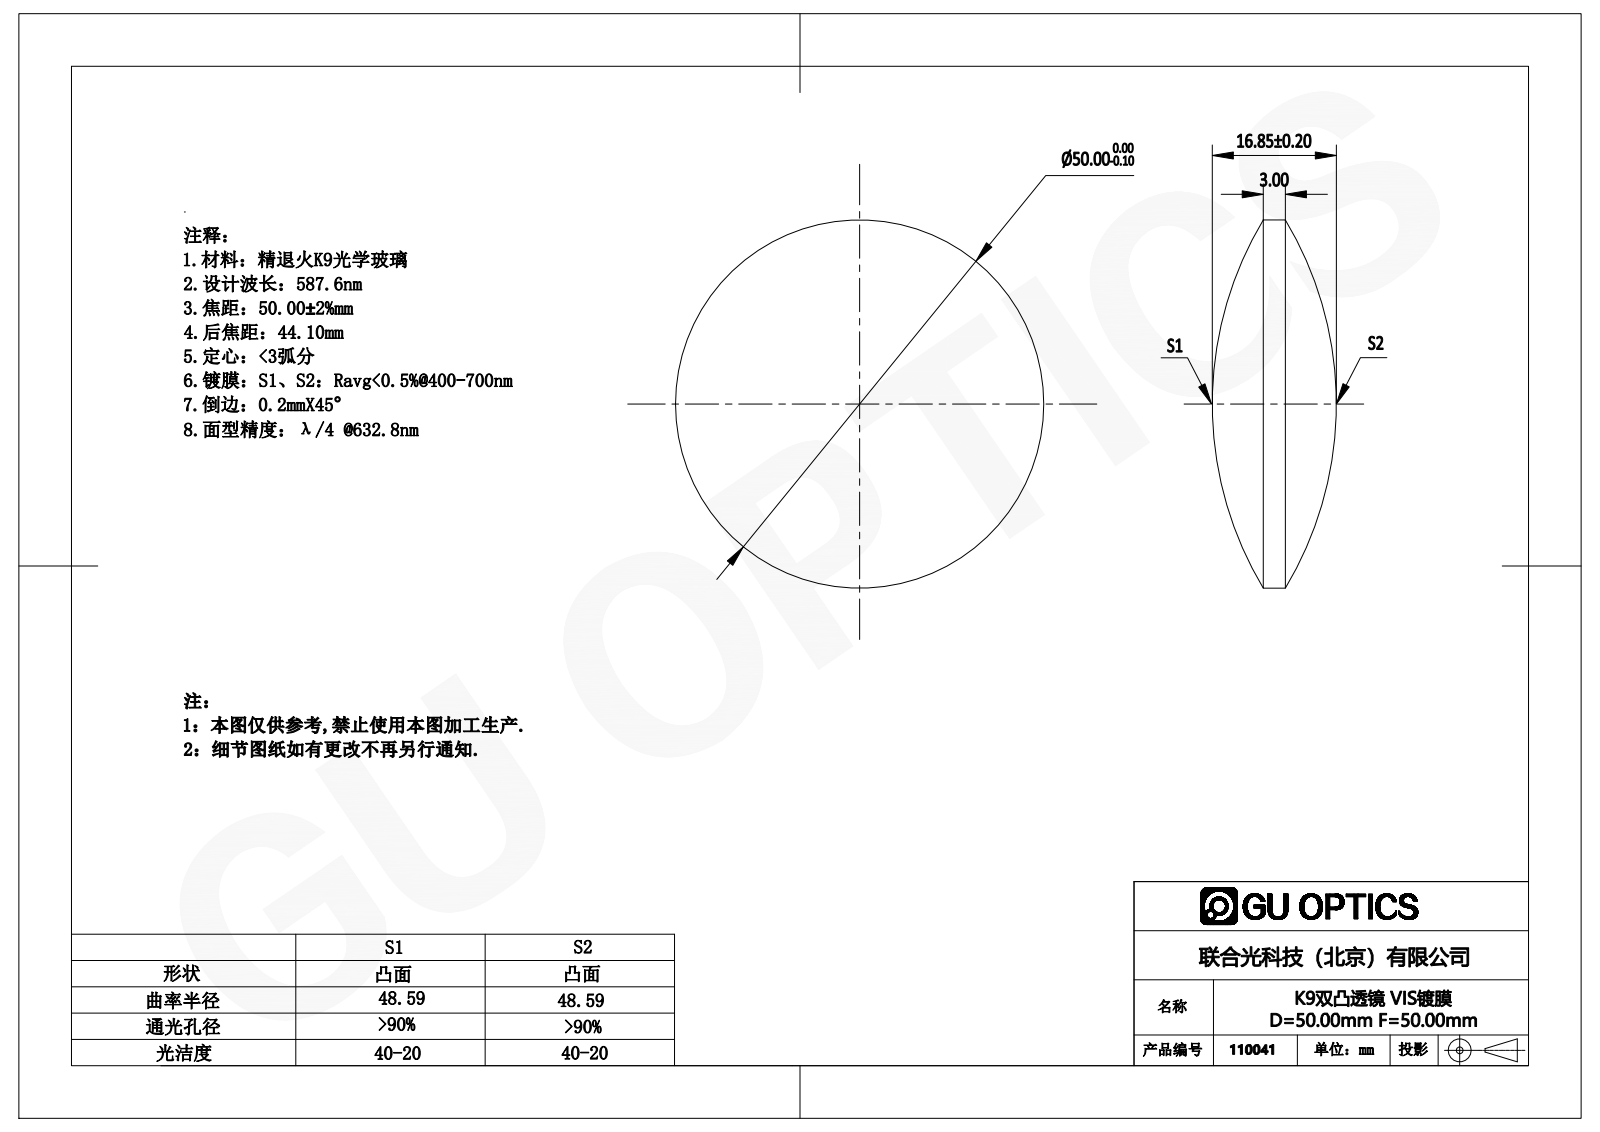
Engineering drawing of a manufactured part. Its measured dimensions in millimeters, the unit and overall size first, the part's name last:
Units: millimetres
Overall size (bounding box): 50 × 50 × 16.85
Round bosses / shafts (diameter × count): ⌀50 ×1
Volume: 19 835 mm³ · Surface area: 4 700 mm²
Bodies: 1 solid, 6 faces (0 planar, 2 cylindrical, 4 other)
Part name (STEP PRODUCT): 110019
STEP written by: SolidWorks 2016 (CONFIG_CONTROL_DESIGN)
